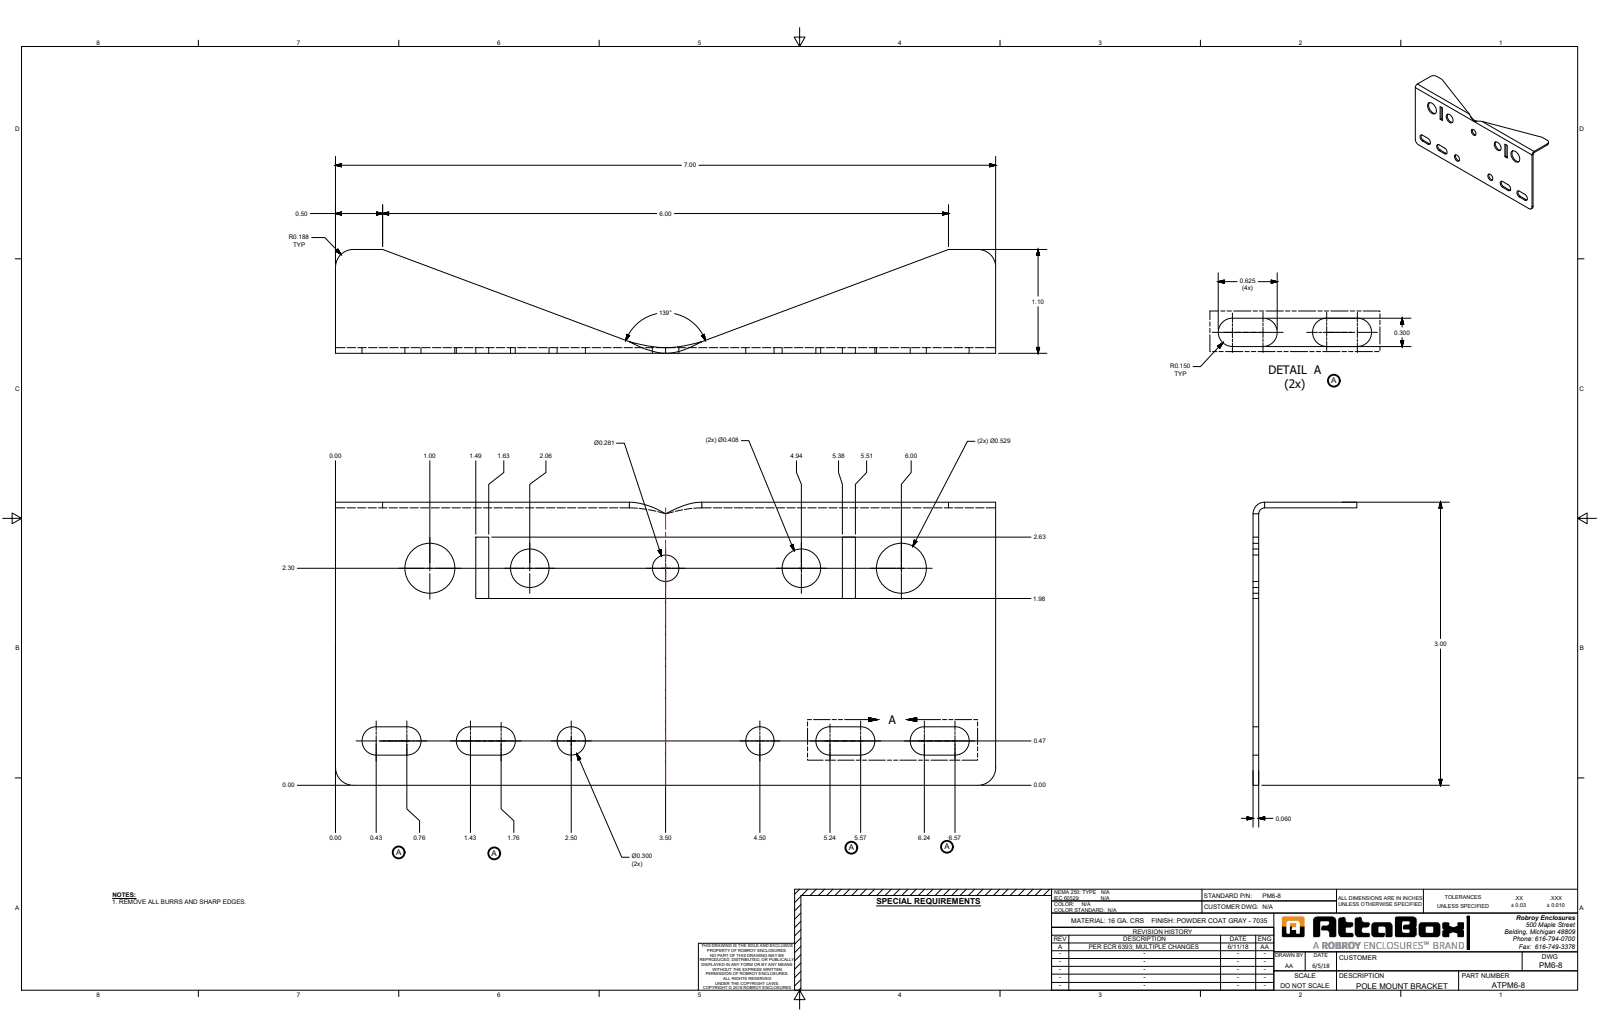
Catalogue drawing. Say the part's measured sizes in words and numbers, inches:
The part is named "35705". Its 3-D file was written by "SolidWorks 2017 (AUTOMOTIVE_DESIGN)". It is 1 solid with 53 faces: 25 planar, 26 cylindrical and 2 other. Overall it measures 7 by 3 by 1.1 inches. Its volume is 1.403 cubic inches and its surface area 48.91 square inches. Round holes: 4 of diameter 0.3, 2 of diameter 0.408, 2 of diameter 0.529, 1 of diameter 0.281. Partial cylindrical surfaces (rounded edges, fillets, slot ends): 2 of radius 0.187, 2 of radius 0.188, 1 of radius 0.063, 1 of radius 0.123. The main face-to-face distances are 0.06, 2.94, 3, 7, 1.487, 5.513, 1.625, 5.375, 0.138, 3.887. The hole center spacings are 1, 1.06, 1.44, 1.856, 1.867, 1.955, 2.287, 2.5.
